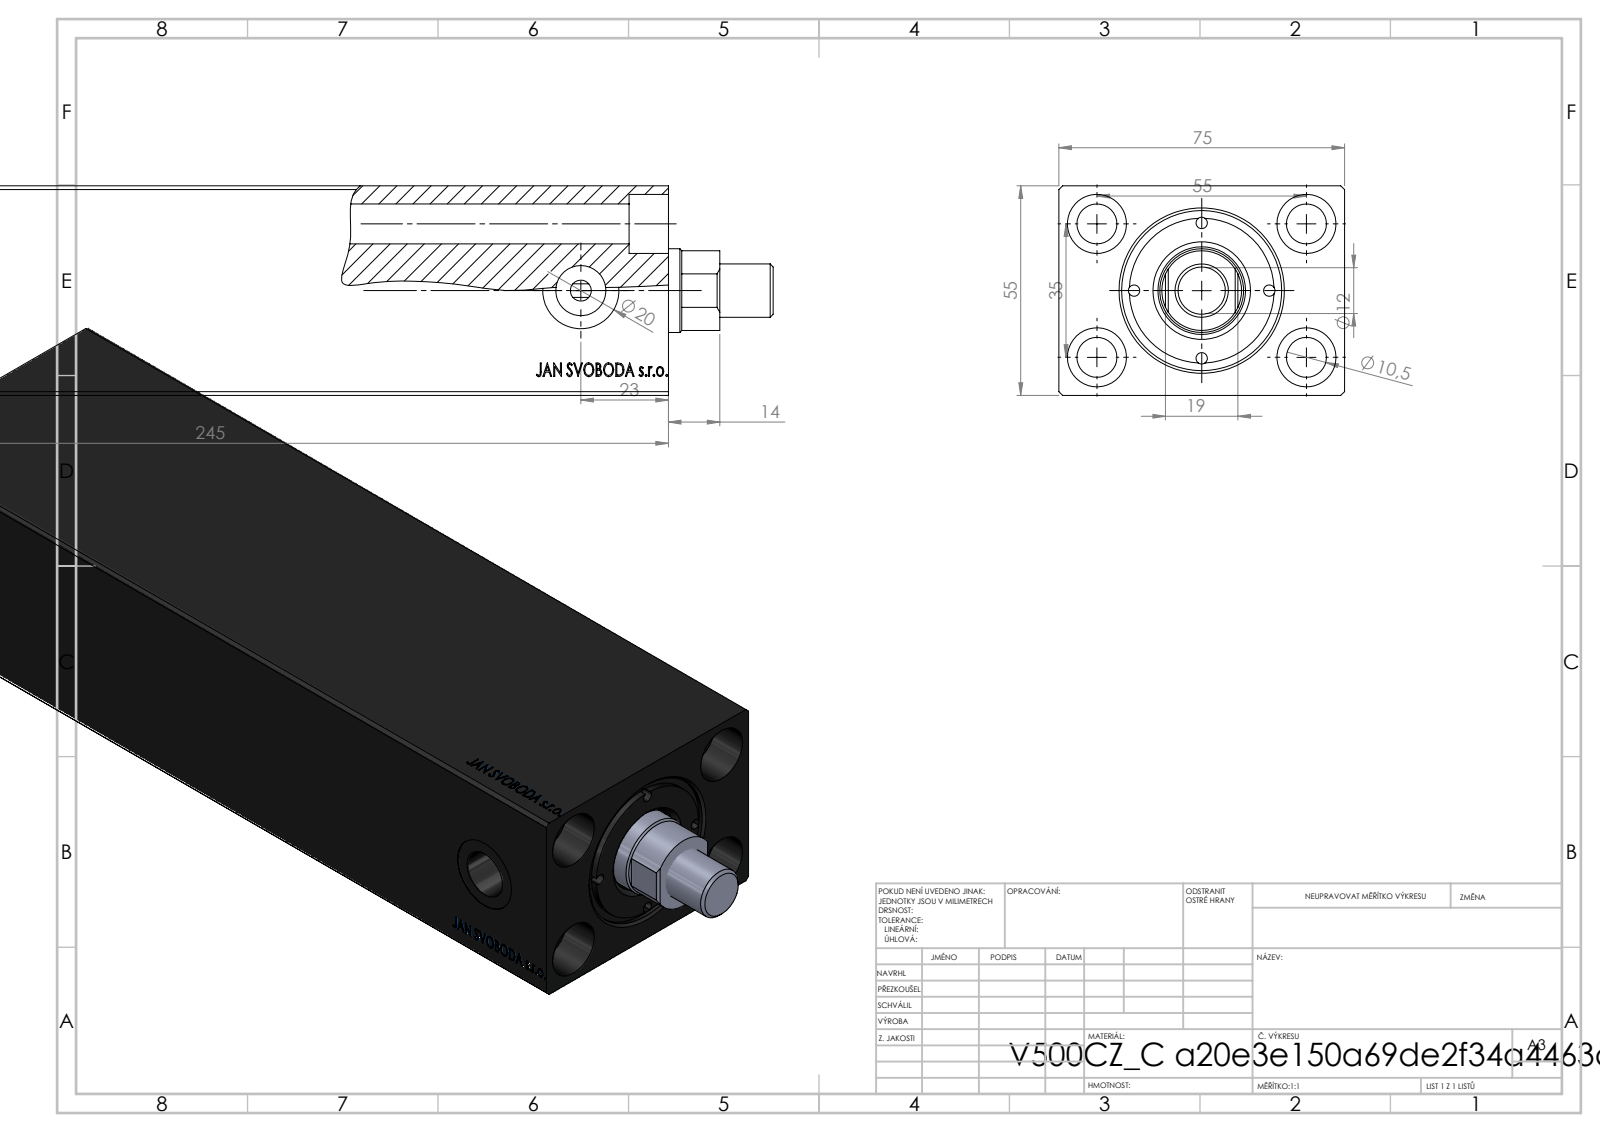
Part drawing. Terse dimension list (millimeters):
name: V500CZ_C; V500CZ_VC_vysunovaci_C; V500CZ_VCP_C; V500CZ_FM
written by: SolidWorks 2019 (CONFIG_CONTROL_DESIGN)
unit: mm
bodies: 4 solids, 904 faces (417 planar, 85 cylindrical, 402 other)
size: 272.5 × 75 × 55
volume: 838 197 mm³; area: 153 584 mm²
holes: 4× ⌀3, 4× ⌀10.5, 4× ⌀15.5, 2× ⌀5.5, 2× ⌀13.16, 2× ⌀13.6, 2× ⌀20, 1× ⌀12, 1× ⌀22, 1× ⌀23, 1× ⌀32, 1× ⌀36
bosses: 1× ⌀38, 1× ⌀14
rounds: 1× R10.46
face distances: 55, 75, 245, 215, 30, 244.8, 29.8, 11.8, 203.2, 233
hole spacings: 17.75, 20.03, 25.1, 27.5, 32.6, 44.71, 48.52, 35
